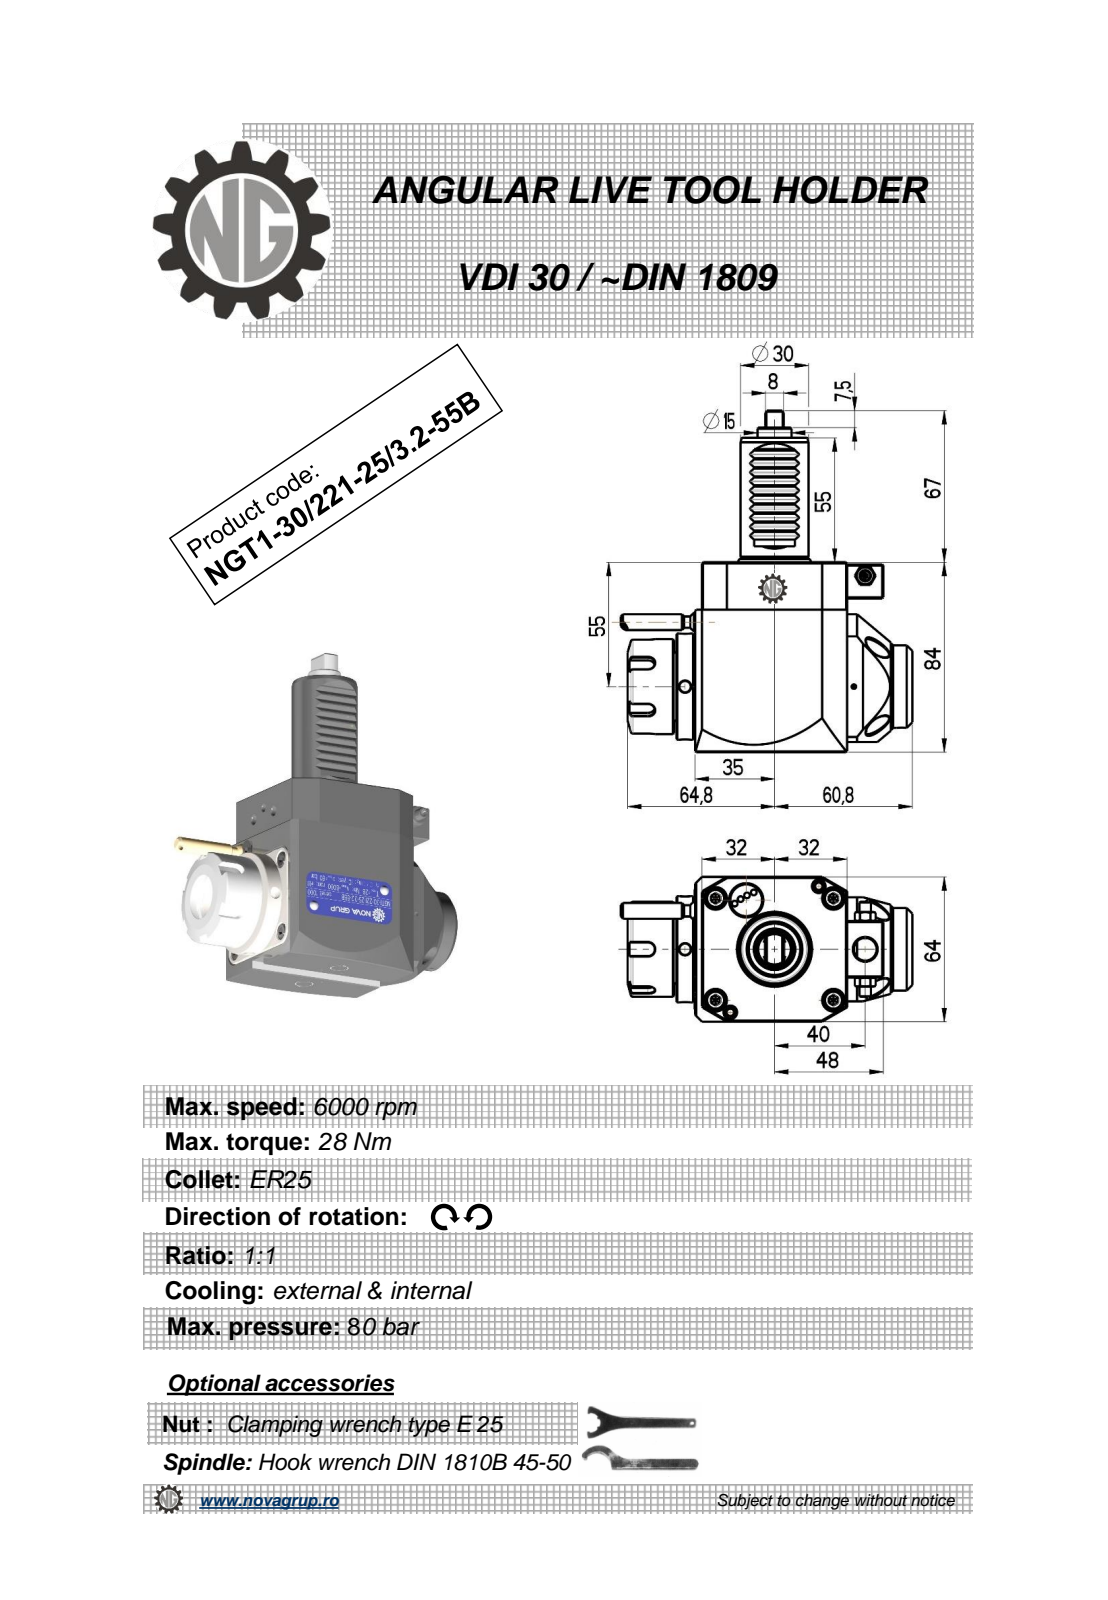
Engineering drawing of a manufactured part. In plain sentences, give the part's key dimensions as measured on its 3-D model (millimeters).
The part is named "NGT1_30_221_25_3_2_55B". Its 3-D file was written by "PRO/ENGINEER BY PARAMETRIC TECHNOLOGY CORPORATION, 2010280 (CONFIG_CONTROL_DESIGN)". It is 1 solid with 429 faces: 195 planar, 86 cylindrical and 148 other. Overall it measures 151 by 128.63 by 64 millimeters. Its volume is 476 706 cubic millimeters and its surface area 48 630 square millimeters. Round holes: 2 of diameter 5, 1 of diameter 2.5, 1 of diameter 3, 1 of diameter 4.2, 1 of diameter 9.5, 1 of diameter 10, 1 of diameter 20.3. Round bosses or shafts: 2 of diameter 8.96, 2 of diameter 5, 1 of diameter 47, 1 of diameter 42, 1 of diameter 36.5, 1 of diameter 35, 1 of diameter 30, 1 of diameter 15. Partial cylindrical surfaces (rounded edges, fillets, slot ends): 12 of radius 0.26, 10 of radius 0.3, 5 of radius 3, 2 of radius 0.8, 2 of radius 160, 1 of radius 7.2, 1 of radius 32. The main face-to-face distances are 64, 84, 0.5, 67.2, 67, 7.5, 3.2, 3, 55, 8. The hole center spacings are 24.76, 33.19, 46.5, 79.45, 93.35.
